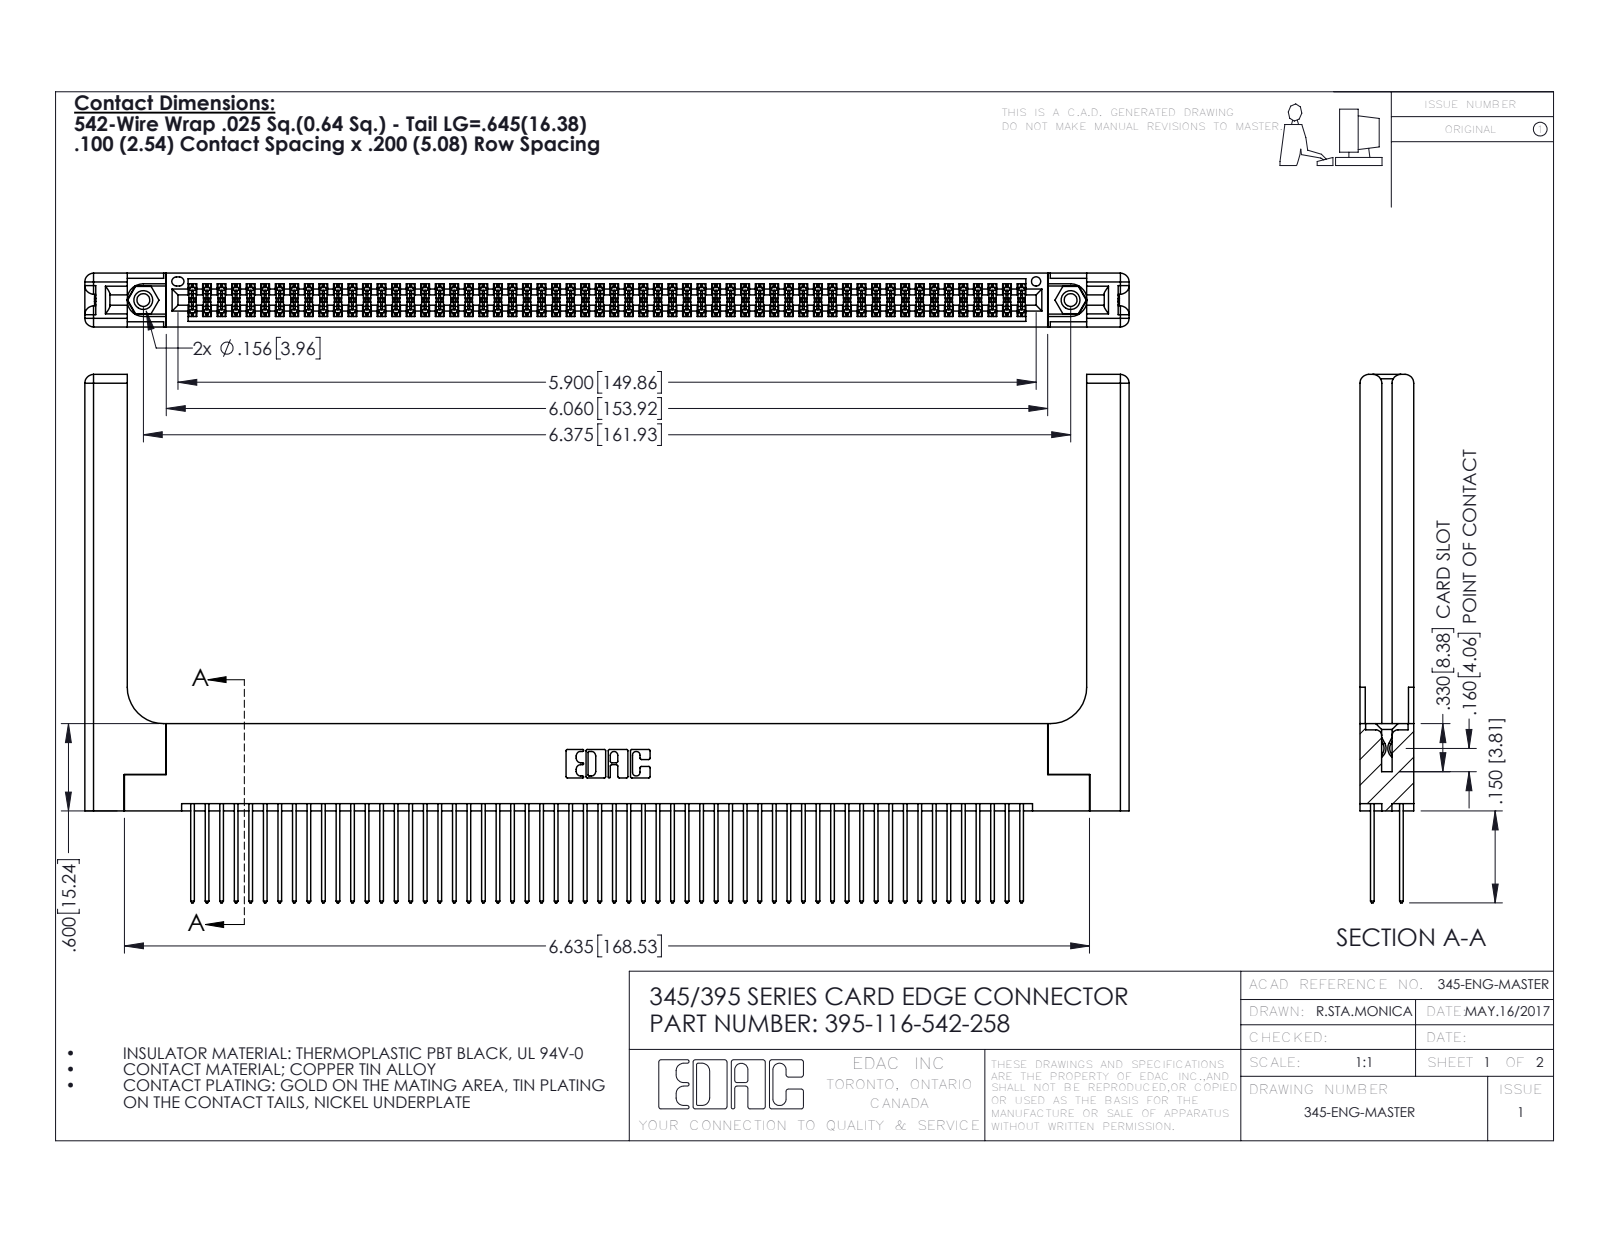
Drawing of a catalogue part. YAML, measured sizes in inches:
part_name: "345-292-001_345-293-142; 345-250-001_345-250-001-102; 345-220-058_345-220-058; 345 Part_Flush Mounting Lugs - 0.156 Dia-TH (+1 more)"
step_written_by: "SolidWorks 2016 (CONFIG_CONTROL_DESIGN)"
units: inches
bodies: {solids: 121, faces: 6182, planar: 4056, cylindrical: 2066, other: 60}
overall_size: [7.179, 3.632, 0.37]
volume: 1.64
surface_area: 54.4
round_holes:
  - {diameter: 0.089, count: 2}
  - {diameter: 0.125, count: 2}
  - {diameter: 0.156, count: 2}
  - {diameter: 0.064, count: 1}
round_bosses_or_shafts:
  - {diameter: 0.155, count: 2}
partial_cylinders:
  - {radius: 0.006, count: 174}
  - {radius: 0.01, count: 116}
  - {radius: 0.01, count: 22}
  - {radius: 0.06, count: 16}
  - {radius: 0.007, count: 6}
  - {radius: 0.031, count: 6}
  - {radius: 0.026, count: 3}
  - {radius: 0.014, count: 2}
face_to_face_distances: [0.072, 0.298, 0.2, 0.37, 0.098, 0.272, 0.025, 0.225, 0.175, 0.148]
hole_center_spacings: [0.27, 6.139, 6.375]
